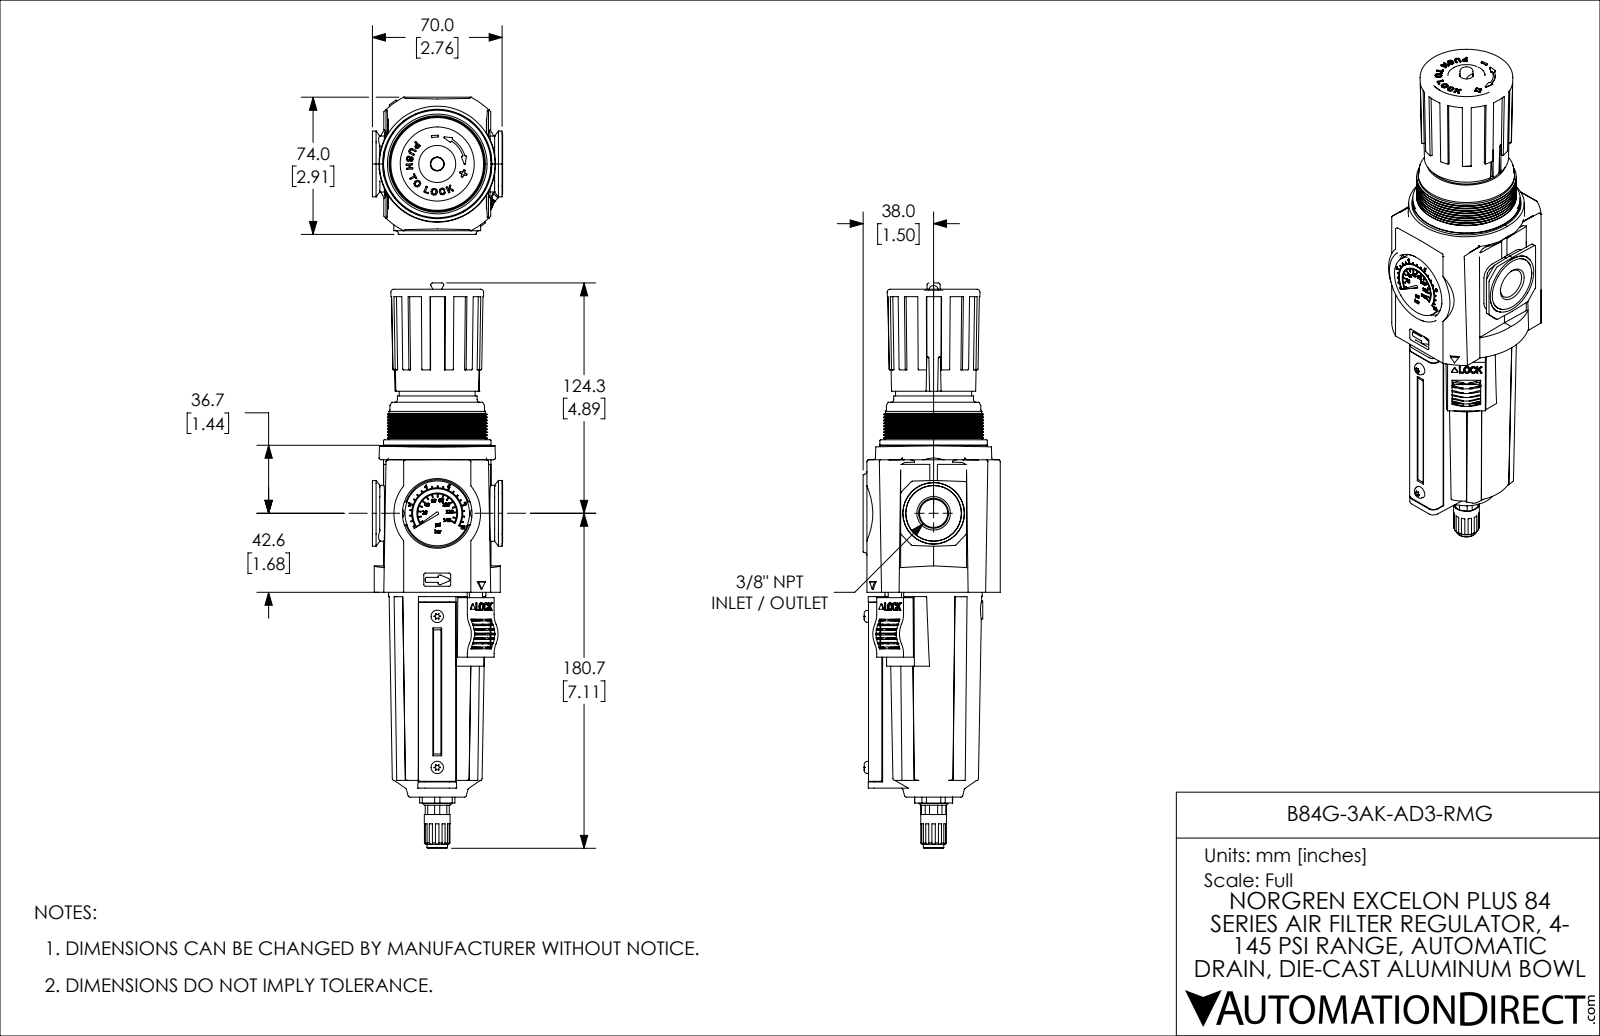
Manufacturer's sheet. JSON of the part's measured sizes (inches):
{"part_name": "B84G-3AK-AD3-RMG", "step_written_by": "SolidWorks 2021 (CONFIG_CONTROL_DESIGN)", "units": "inches", "bodies": {"solids": 9, "faces": 2717, "planar": 1003, "cylindrical": 1241, "other": 473}, "overall_size": [12.005, 2.913, 2.766], "volume_in3": 46.77, "surface_area_in2": 225, "round_holes": [[0.112, 2], [0.177, 2], [0.059, 1], [0.197, 1], [0.22, 1], [0.246, 1], [0.633, 1], [0.776, 1], [1.319, 1], [2.323, 1], [2.461, 1]], "round_bosses_or_shafts": [[0.299, 2], [0.213, 2], [0.157, 2], [2.283, 1], [2.122, 1], [2.119, 1], [2.067, 1], [2.047, 1]], "partial_cylinders_radius": [[0.039, 48], [0.028, 28], [0.012, 27], [0.02, 23], [0.01, 18], [0.047, 18], [0.03, 16], [0.004, 14]], "face_to_face_distances": [2.719, 2.323, 2.457, 0.512, 0.364, 2.354, 0.622, 0.134, 2.096, 1.732], "hole_center_spacings": [0.856, 2.685, 5.121, 1.713, 2.504, 2.545, 5.049]}
